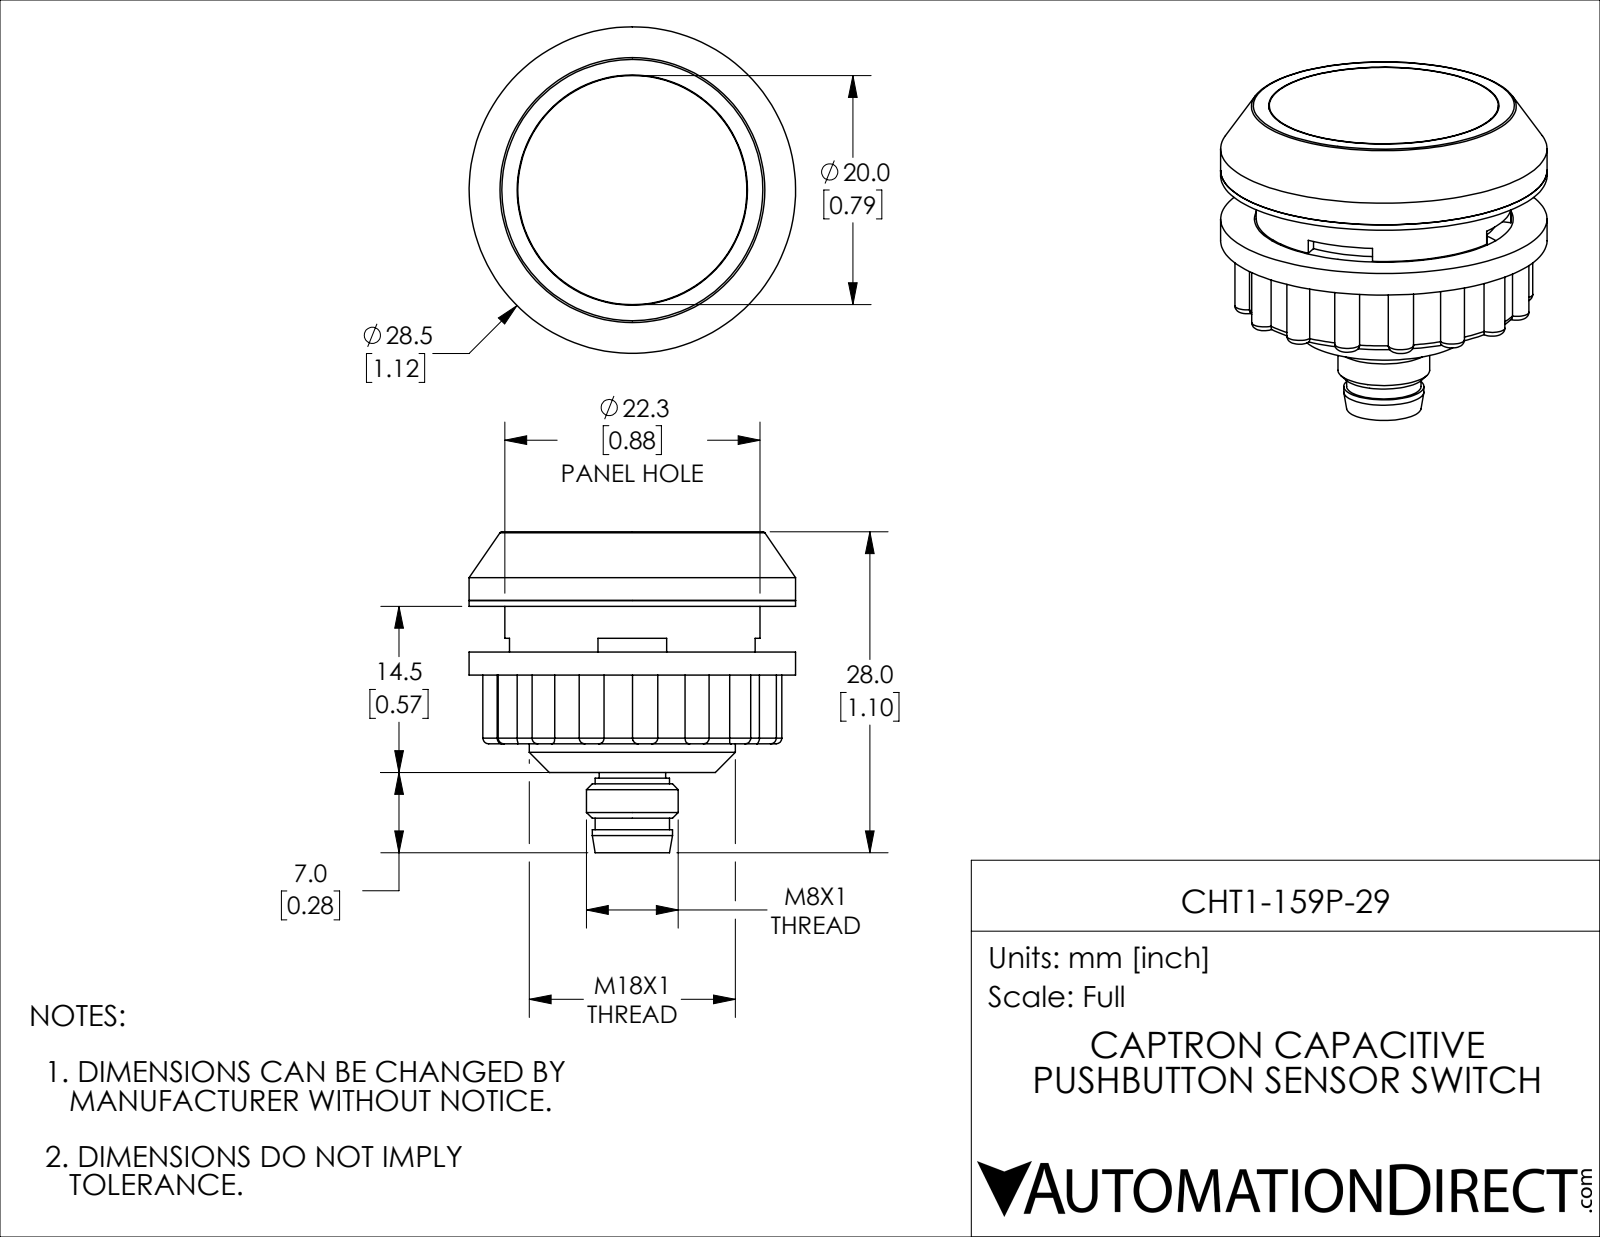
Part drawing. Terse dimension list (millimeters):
name: CHT1-159P-29
written by: SolidWorks 2019 (CONFIG_CONTROL_DESIGN)
unit: mm
bodies: 10 solids, 212 faces (40 planar, 97 cylindrical, 75 other)
size: 28.5 × 28.5 × 28
volume: 10 506 mm³; area: 7 381 mm²
holes: 2× ⌀2, 1× ⌀6, 1× ⌀17, 1× ⌀20.1, 1× ⌀22.22, 1× ⌀22.6
bosses: 4× ⌀1, 1× ⌀28.5, 1× ⌀22.28, 1× ⌀19.08, 1× ⌀18, 1× ⌀8, 1× ⌀7, 1× ⌀6.5
rounds: 16× R1.1, 1× R9.9, 1× R12
face distances: 3, 6, 0.5, 6.5, 3.5, 10.5, 4, 2.5, 4.5, 15
hole spacings: 5.5, 11
